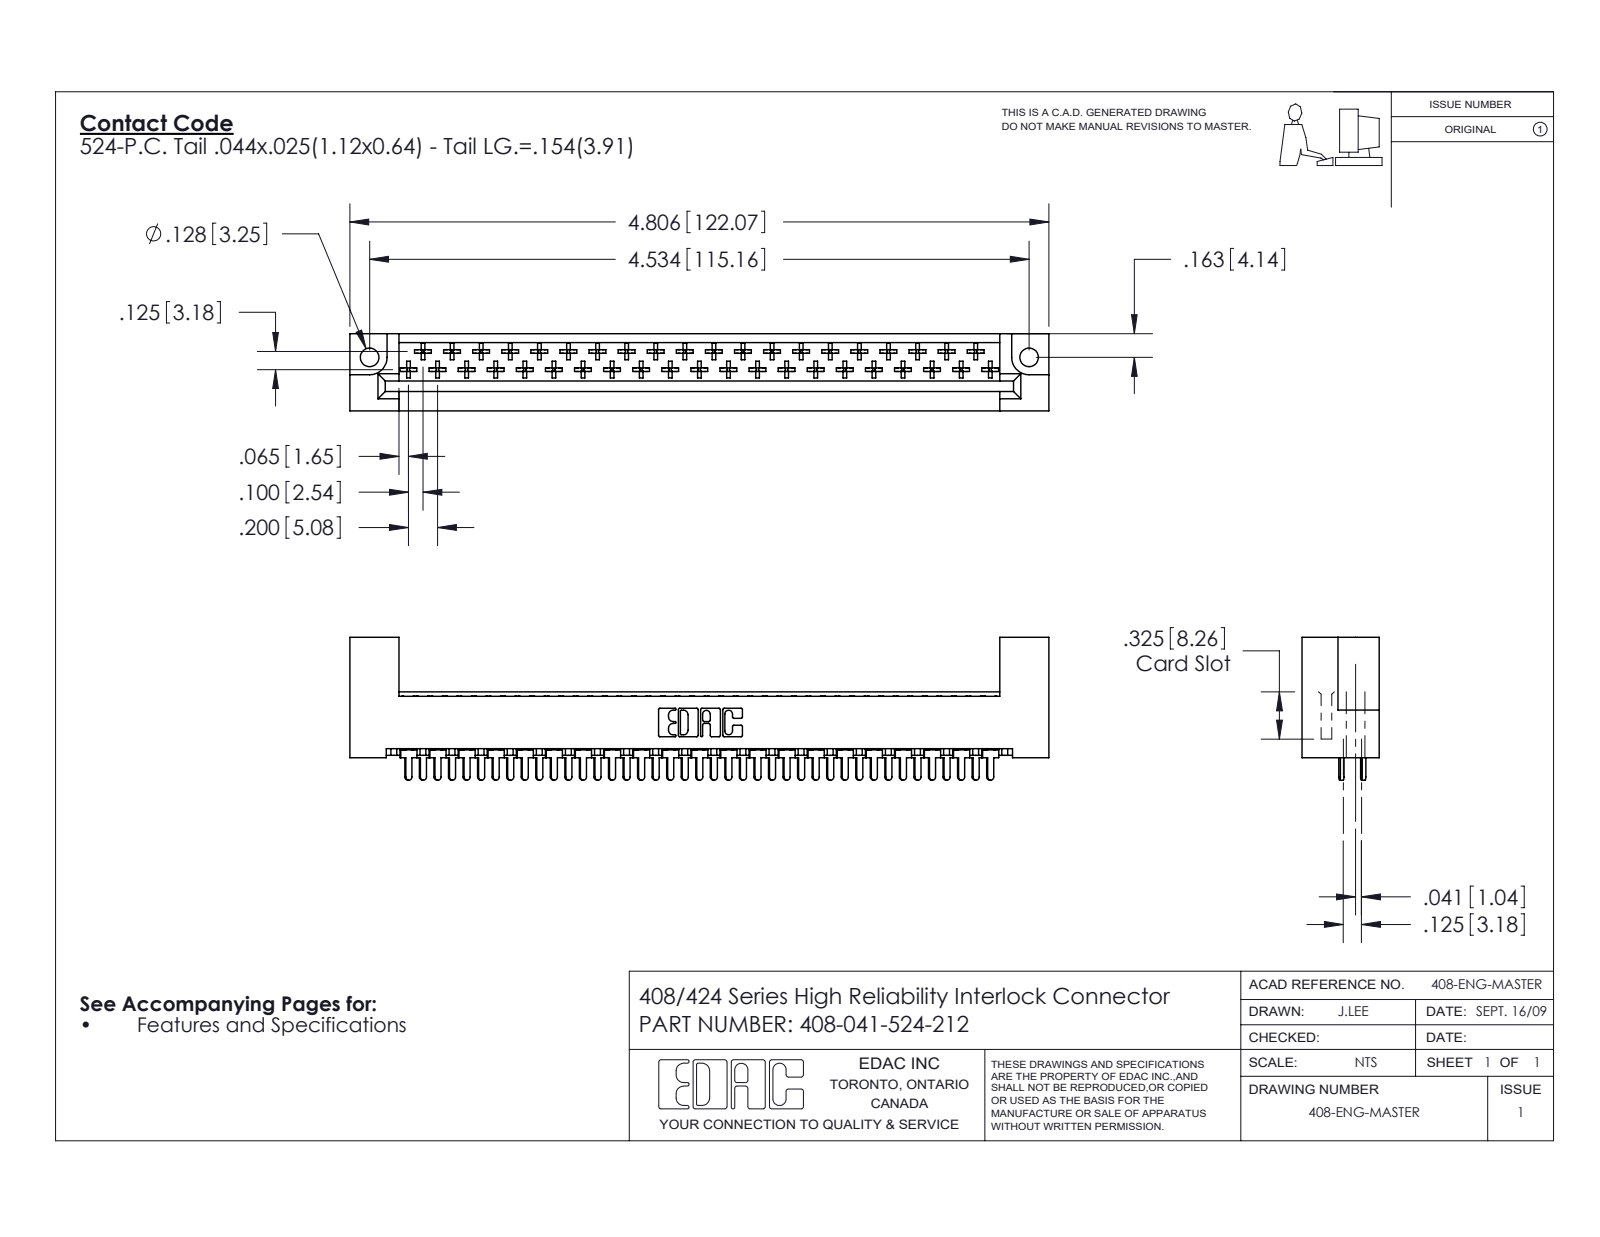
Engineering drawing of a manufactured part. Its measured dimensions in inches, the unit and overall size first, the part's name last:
Units: inches
Overall size (bounding box): 4.806 × 0.982 × 0.531
Round holes (diameter × count): ⌀0.128 ×2
Partial cylindrical surfaces — rounded edges, fillets, slot ends (radius × count): R0.01 ×246, R0.02 ×43, R0.022 ×41, R0.01 ×22, R0.007 ×6, R0.031 ×6, R0.026 ×3, R0.12 ×2
Main face-to-face distances: 0.531, 0.125, 0.025, 0.1, 0.025, 0.361, 0.235, 0.259, 0.398, 0.217
Hole centre spacings: 4.534
Volume: 0.917 in³ · Surface area: 27.35 in²
Bodies: 42 solids, 2394 faces (1811 planar, 419 cylindrical, 164 other)
Part name (STEP PRODUCT): 408-047-524-212; 408-290-001_408-290-124 - Bottom; 408-290-001_408-290-124 - Top; 408 Part_041 - 2
STEP written by: SolidWorks 2016 (CONFIG_CONTROL_DESIGN)
